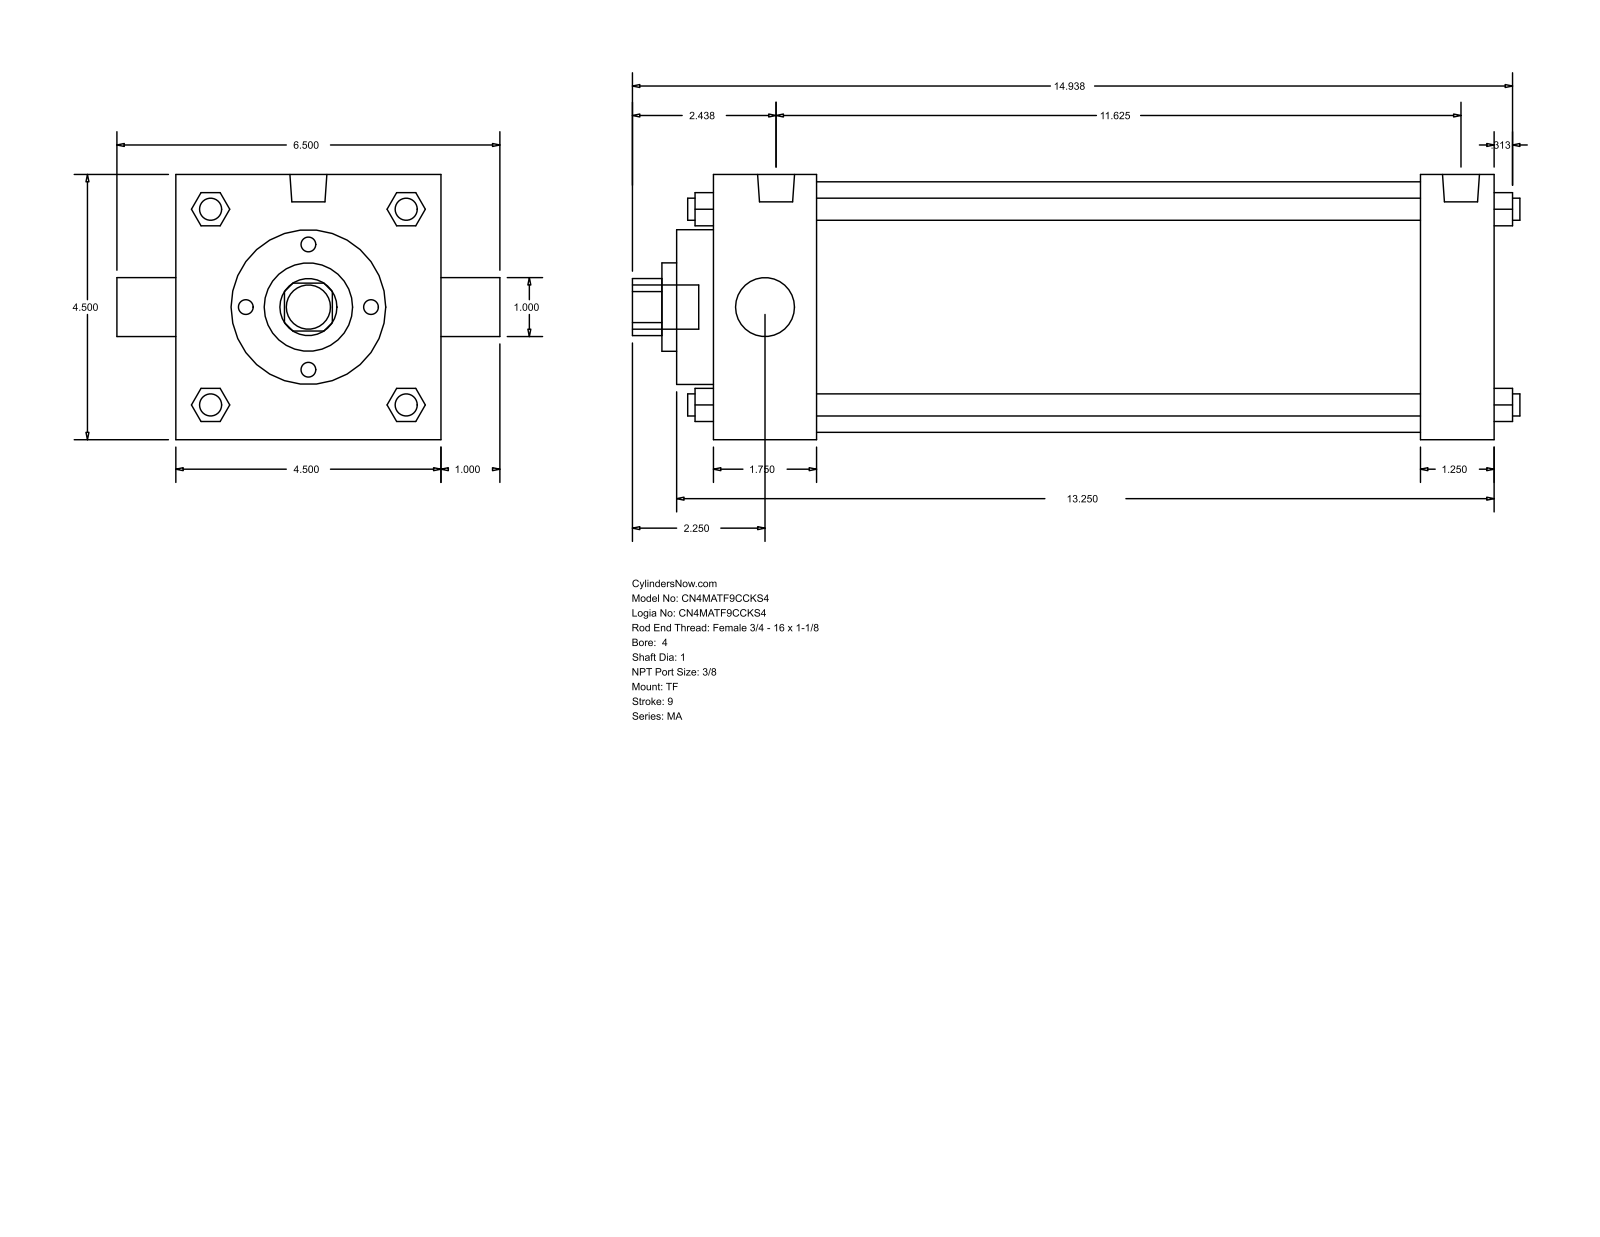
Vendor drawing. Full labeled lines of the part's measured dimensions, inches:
Part name (STEP PRODUCT): MA_TF__0400_1
STEP written by: GSSL Pune (CONFIG_CONTROL_DESIGN)
Units: inches
Bodies: 0 solids, 122 faces (93 planar, 29 cylindrical, 0 other)
Overall size (bounding box): 15.063 × 6.5 × 4.5
Round holes (diameter × count): ⌀1 ×2, ⌀1.5 ×1, ⌀2.625 ×1, ⌀4.25 ×1
Round bosses / shafts (diameter × count): ⌀0.375 ×4, ⌀0.437 ×3, ⌀0.627 ×2, ⌀0.75 ×1
Partial cylindrical surfaces — rounded edges, fillets, slot ends (radius × count): R0.484 ×1
Main face-to-face distances: 4.5, 13.25, 12, 1.25, 1.75, 10.25, 11.5, 0.625, 2.375, 12.625
